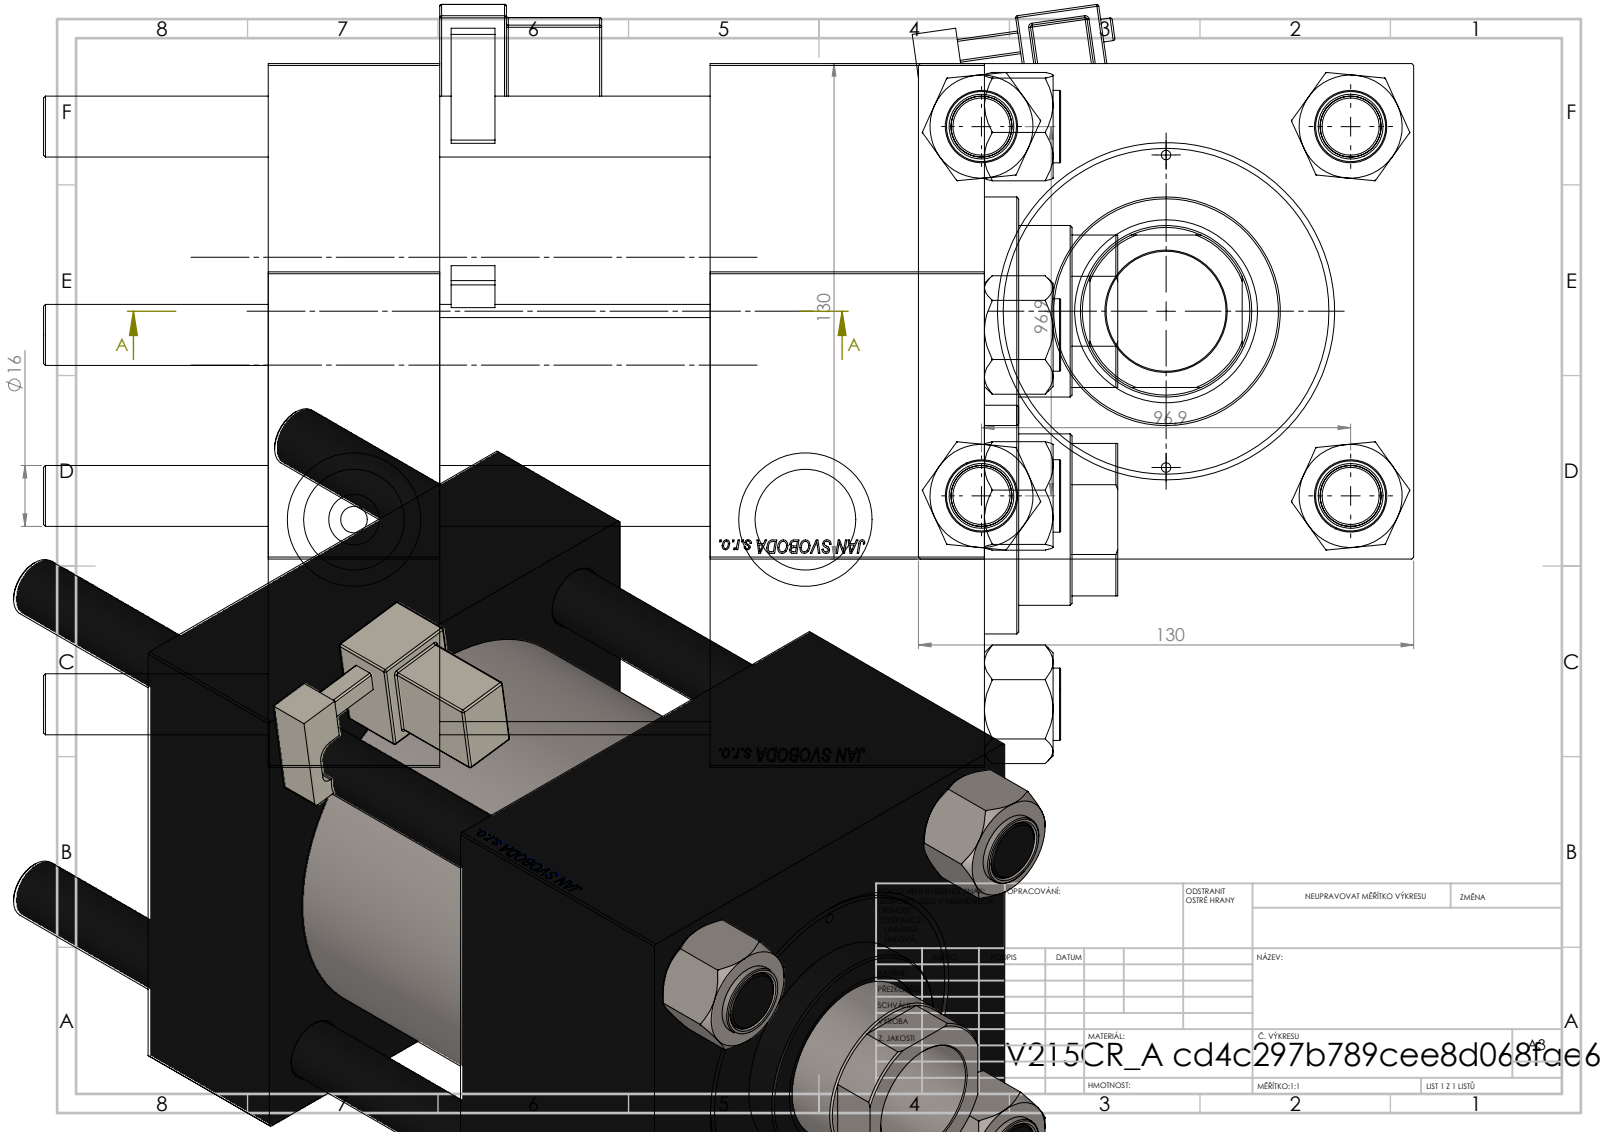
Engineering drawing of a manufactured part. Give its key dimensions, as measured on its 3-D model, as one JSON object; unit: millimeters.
{"part_name": "V215_VC_A; NUT_M5; CR025_012_A_0_G_A_G_M_020_+#_##_TYCINKA; V215CR_MSU (+2 more)", "step_written_by": "SolidWorks 2019 (CONFIG_CONTROL_DESIGN)", "units": "millimeters", "bodies": {"solids": 12, "faces": 1265, "planar": 599, "cylindrical": 112, "other": 554}, "overall_size": [282, 145.5, 131.61], "volume_mm3": 2525000, "surface_area_mm2": 359915, "round_holes": [[16, 4], [2.5, 2], [7, 2], [26.44, 2], [35, 2], [31.5, 1], [45, 1], [48, 1], [76, 1], [85.5, 1], [100, 1]], "round_bosses_or_shafts": [[19, 4], [106, 1], [60, 1], [6, 1]], "partial_cylinders_radius": [[0.5, 24], [1, 1], [2.5, 1], [4, 1], [22, 1]], "face_to_face_distances": [130, 45, 188, 143, 116, 71, 72, 20, 92, 96], "hole_center_spacings": [49.02, 68.52, 96.9, 101.73, 41, 137.04, 82, 118.5]}
